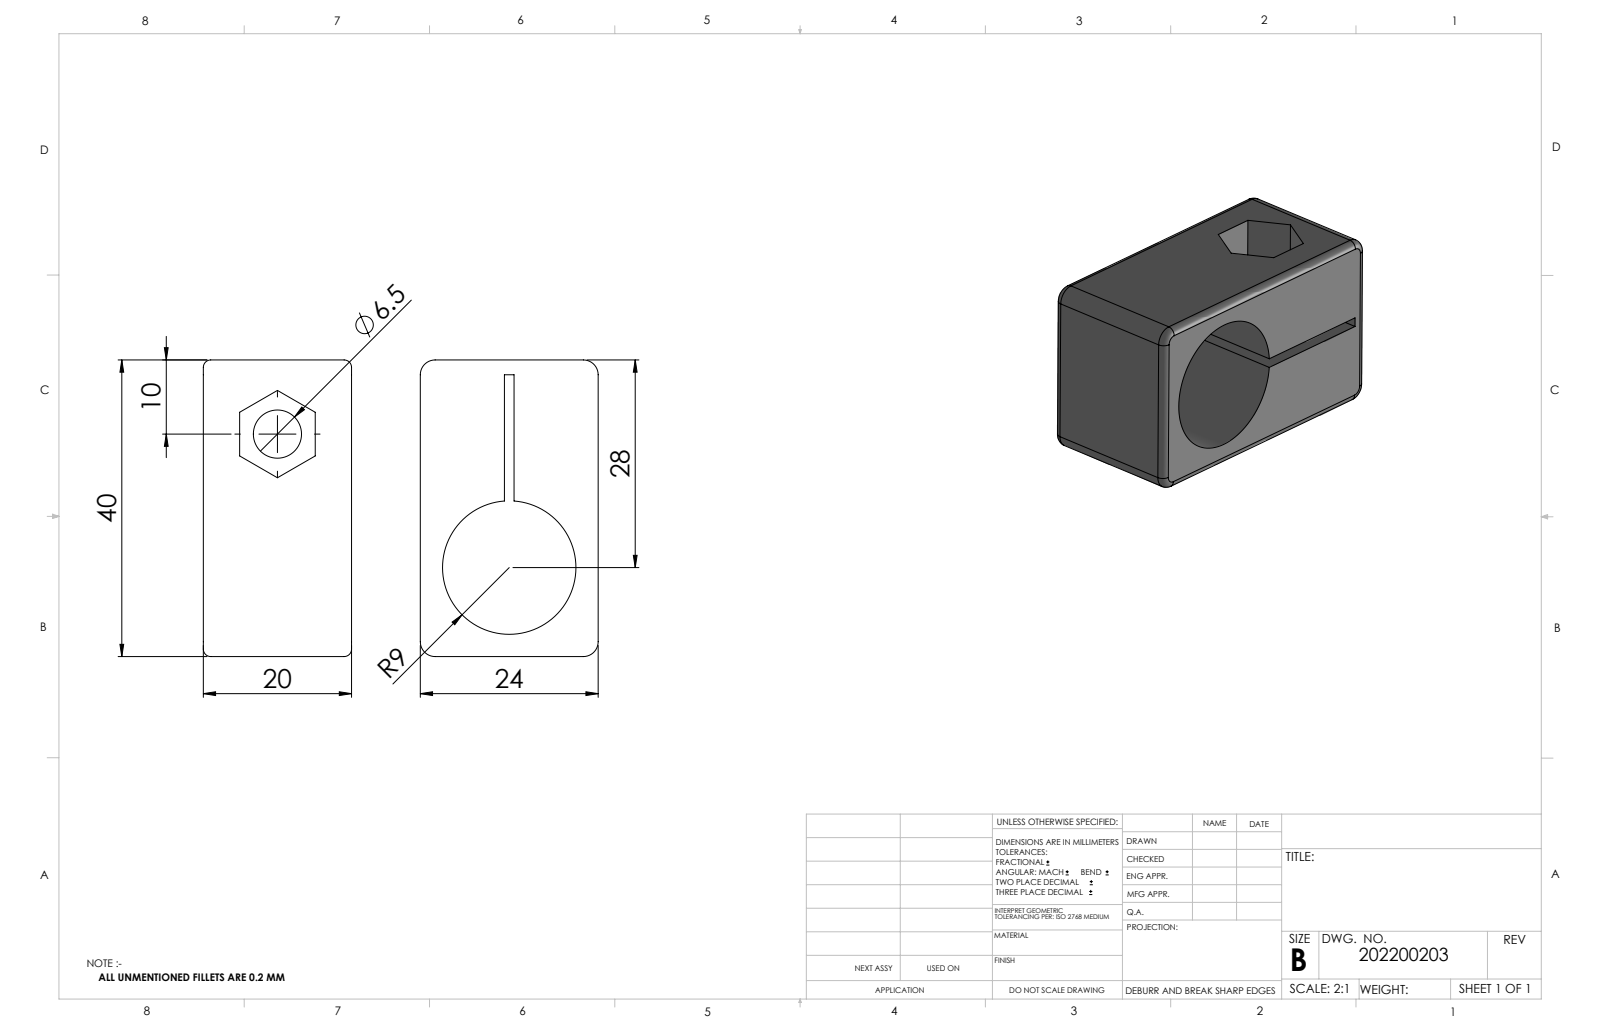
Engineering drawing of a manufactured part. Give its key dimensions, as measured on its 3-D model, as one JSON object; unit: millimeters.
{"part_name": "202200203_c_1", "step_written_by": "SolidWorks 2014 (CONFIG_CONTROL_DESIGN)", "units": "millimeters", "bodies": {"solids": 1, "faces": 49, "planar": 18, "cylindrical": 23, "other": 8}, "overall_size": [40, 24, 20], "volume_mm3": 12090, "surface_area_mm2": 6048, "round_holes": [[6.5, 1], [10, 1], [16, 1], [18, 1]], "partial_cylinders_radius": [[1, 8], [2, 4]], "face_to_face_distances": [11.35, 12.65, 20, 24, 40, 1.3, 1.5, 9.85, 11.15, 22.5]}
